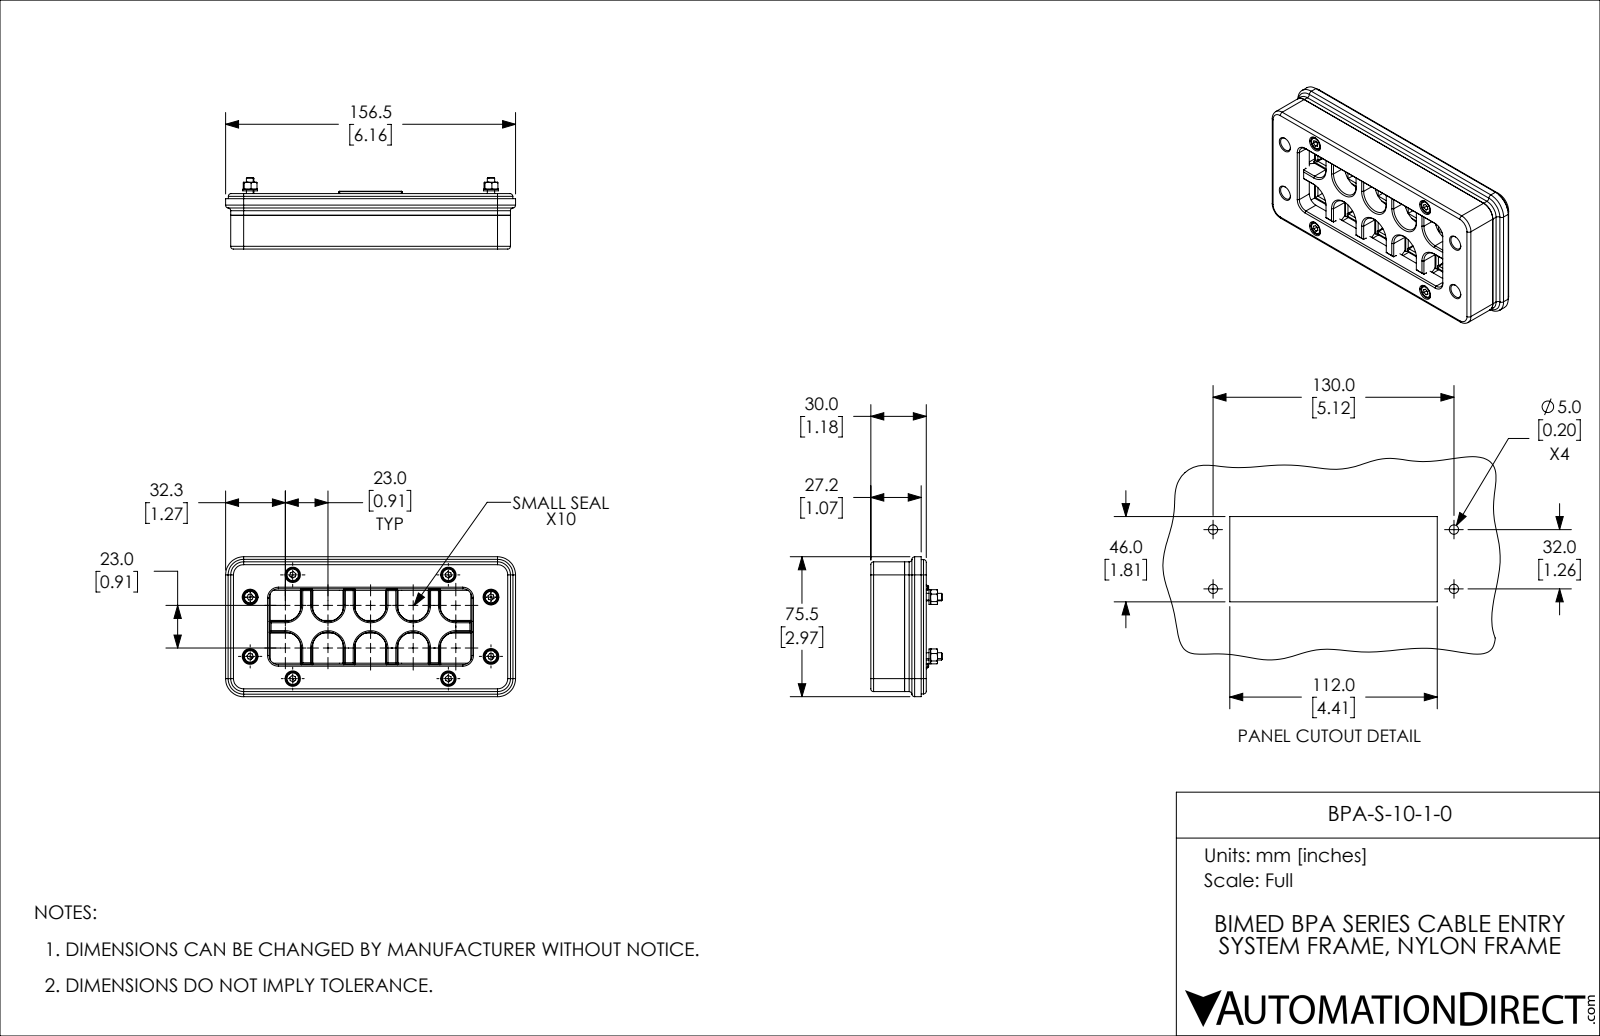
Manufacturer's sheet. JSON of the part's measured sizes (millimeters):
{"part_name": "BPA-S-10-1-0", "step_written_by": "SolidWorks 2021 (CONFIG_CONTROL_DESIGN)", "units": "millimeters", "bodies": {"solids": 29, "faces": 1822, "planar": 894, "cylindrical": 574, "other": 354}, "overall_size": [156.5, 75.5, 38.6], "volume_mm3": 188595, "surface_area_mm2": 99126, "round_holes": [[4.5, 8], [3.24, 7], [4.3, 4], [5, 4], [7.3, 4], [7.5, 4], [8, 4]], "round_bosses_or_shafts": [[7, 8], [4, 8], [8.1, 4], [8, 4], [6.9, 4]], "partial_cylinders_radius": [[0.5, 59], [1.5, 20], [1, 18], [0.4, 10], [0.75, 10], [1.25, 4], [3.4, 4], [3.5, 4]], "face_to_face_distances": [2.25, 2.5, 67.75, 27.2, 3, 8.4, 18.8, 9.6, 67.5, 65.25], "hole_center_spacings": [25.94, 49.65, 107.67, 115.69, 32, 56, 84, 100.96]}
